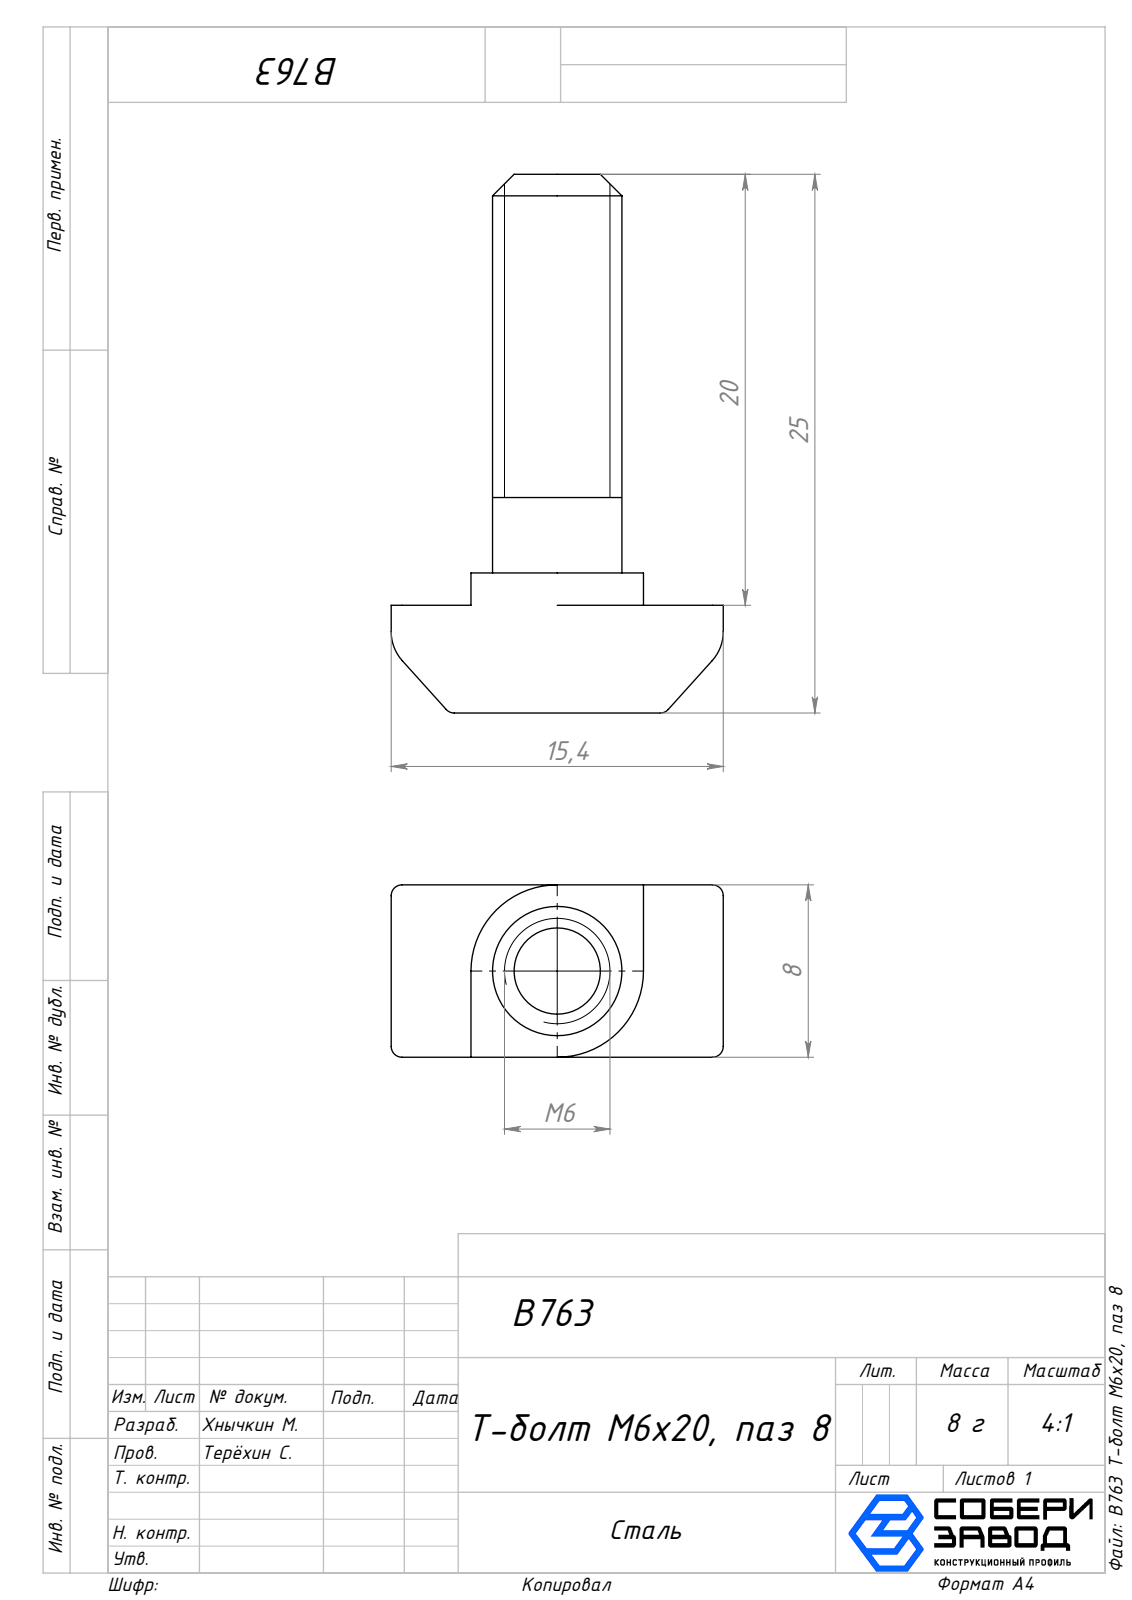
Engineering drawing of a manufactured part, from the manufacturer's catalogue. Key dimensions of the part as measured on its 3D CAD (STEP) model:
Part name (STEP PRODUCT): B763 Т-болт М6х20, паз 8
STEP written by: SolidWorks 2025 (AUTOMOTIVE_DESIGN)
Units: millimetres
Bodies: 1 solid, 41 faces (13 planar, 18 cylindrical, 10 other)
Overall size (bounding box): 25 × 15.4 × 8
Volume: 1 148 mm³ · Surface area: 805 mm²
Round bosses / shafts (diameter × count): ⌀6 ×1
Partial cylindrical surfaces — rounded edges, fillets, slot ends (radius × count): R0.5 ×12, R2 ×2, R4 ×1
Main face-to-face distances: 8, 5, 6.5, 1.5, 25, 20, 18.5, 3.7, 11.7, 15.4
